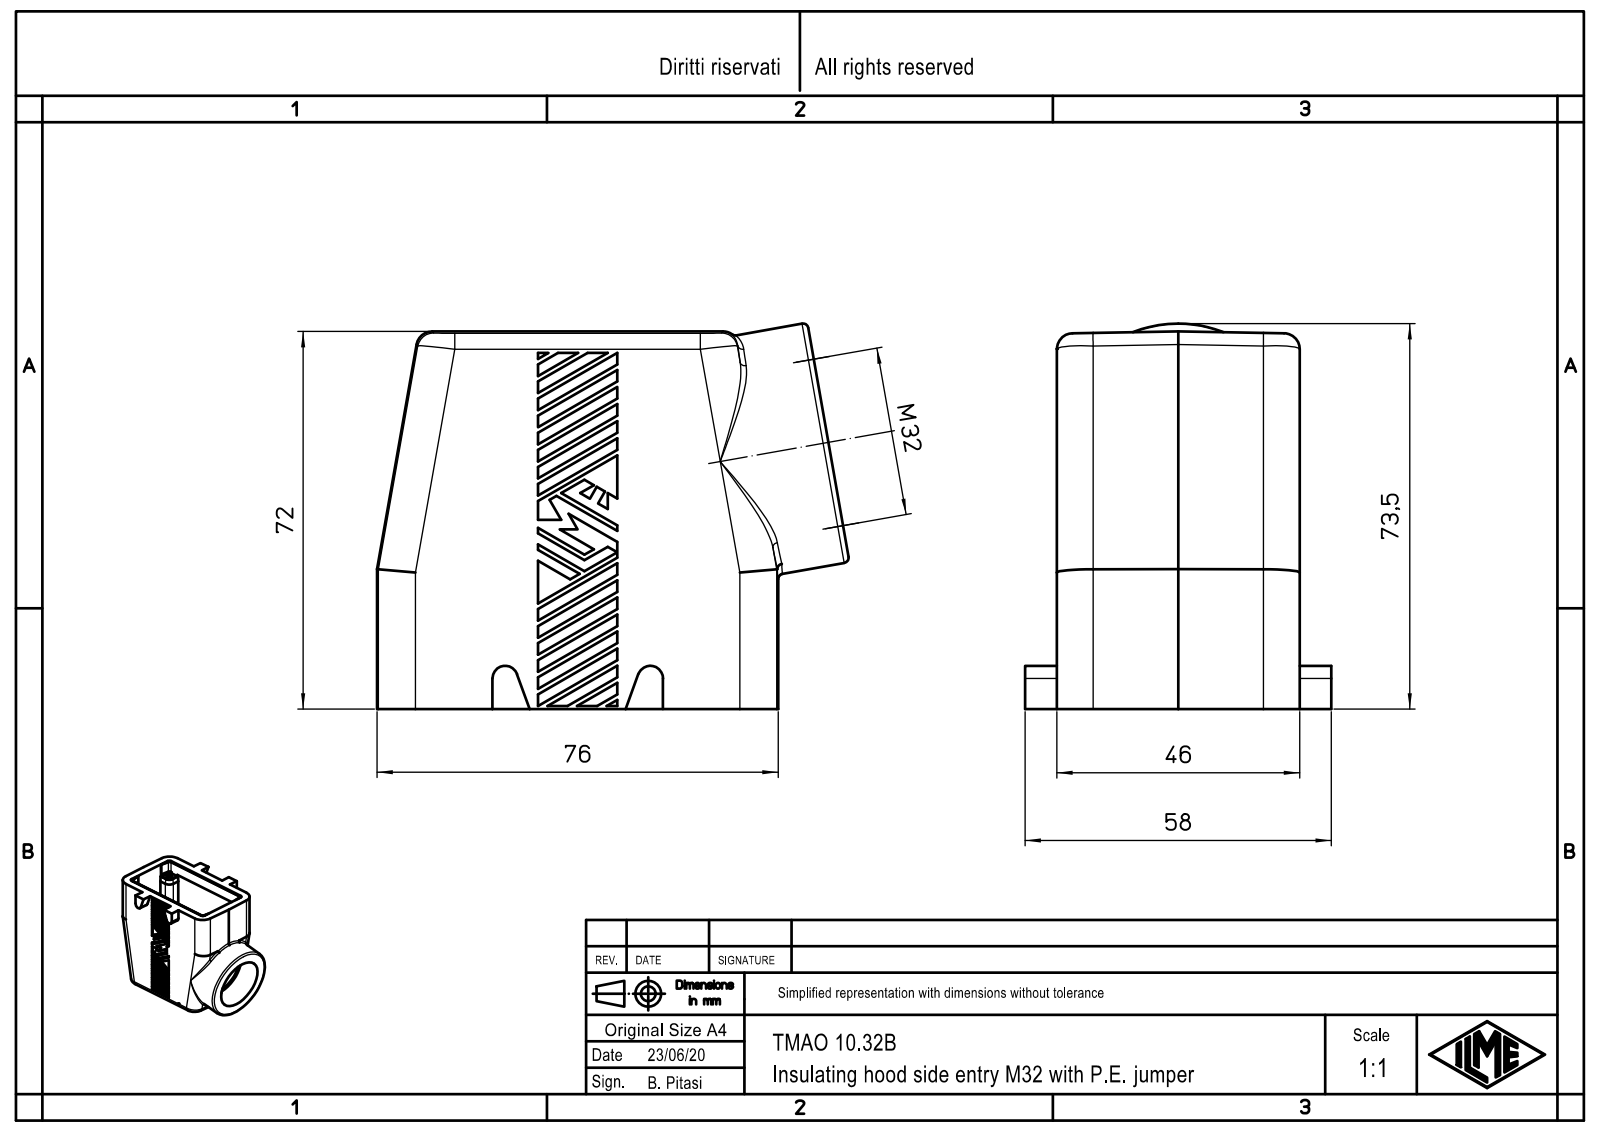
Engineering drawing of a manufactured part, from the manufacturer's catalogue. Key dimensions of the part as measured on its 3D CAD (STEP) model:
Part name (STEP PRODUCT): TMAO_10.32B
STEP written by: Creo Elements/Direct Modeling 20.1B 02-Apr-2019 (C) Parametric Technology GmbH (AUTOMOTIVE_DESIGN)
Units: millimetres
Bodies: 1 solid, 571 faces (402 planar, 83 cylindrical, 86 other)
Overall size (bounding box): 89.33 × 72.98 × 58
Volume: 111 118 mm³ · Surface area: 41 282 mm²
Round holes (diameter × count): ⌀3 ×4, ⌀3.5 ×4, ⌀28 ×1, ⌀32 ×1
Round bosses / shafts (diameter × count): ⌀4.8 ×4, ⌀46 ×1
Partial cylindrical surfaces — rounded edges, fillets, slot ends (radius × count): R1.5 ×12, R7 ×8, R3 ×6, R1.3 ×4, R1.6 ×4, R2 ×4, R3.5 ×4, R2.4 ×2
Main face-to-face distances: 46, 65.99, 0.5, 45.5, 5.6, 6.1, 5.3, 5.8, 40.2, 39.7
Hole centre spacings: 27, 57, 63.07
